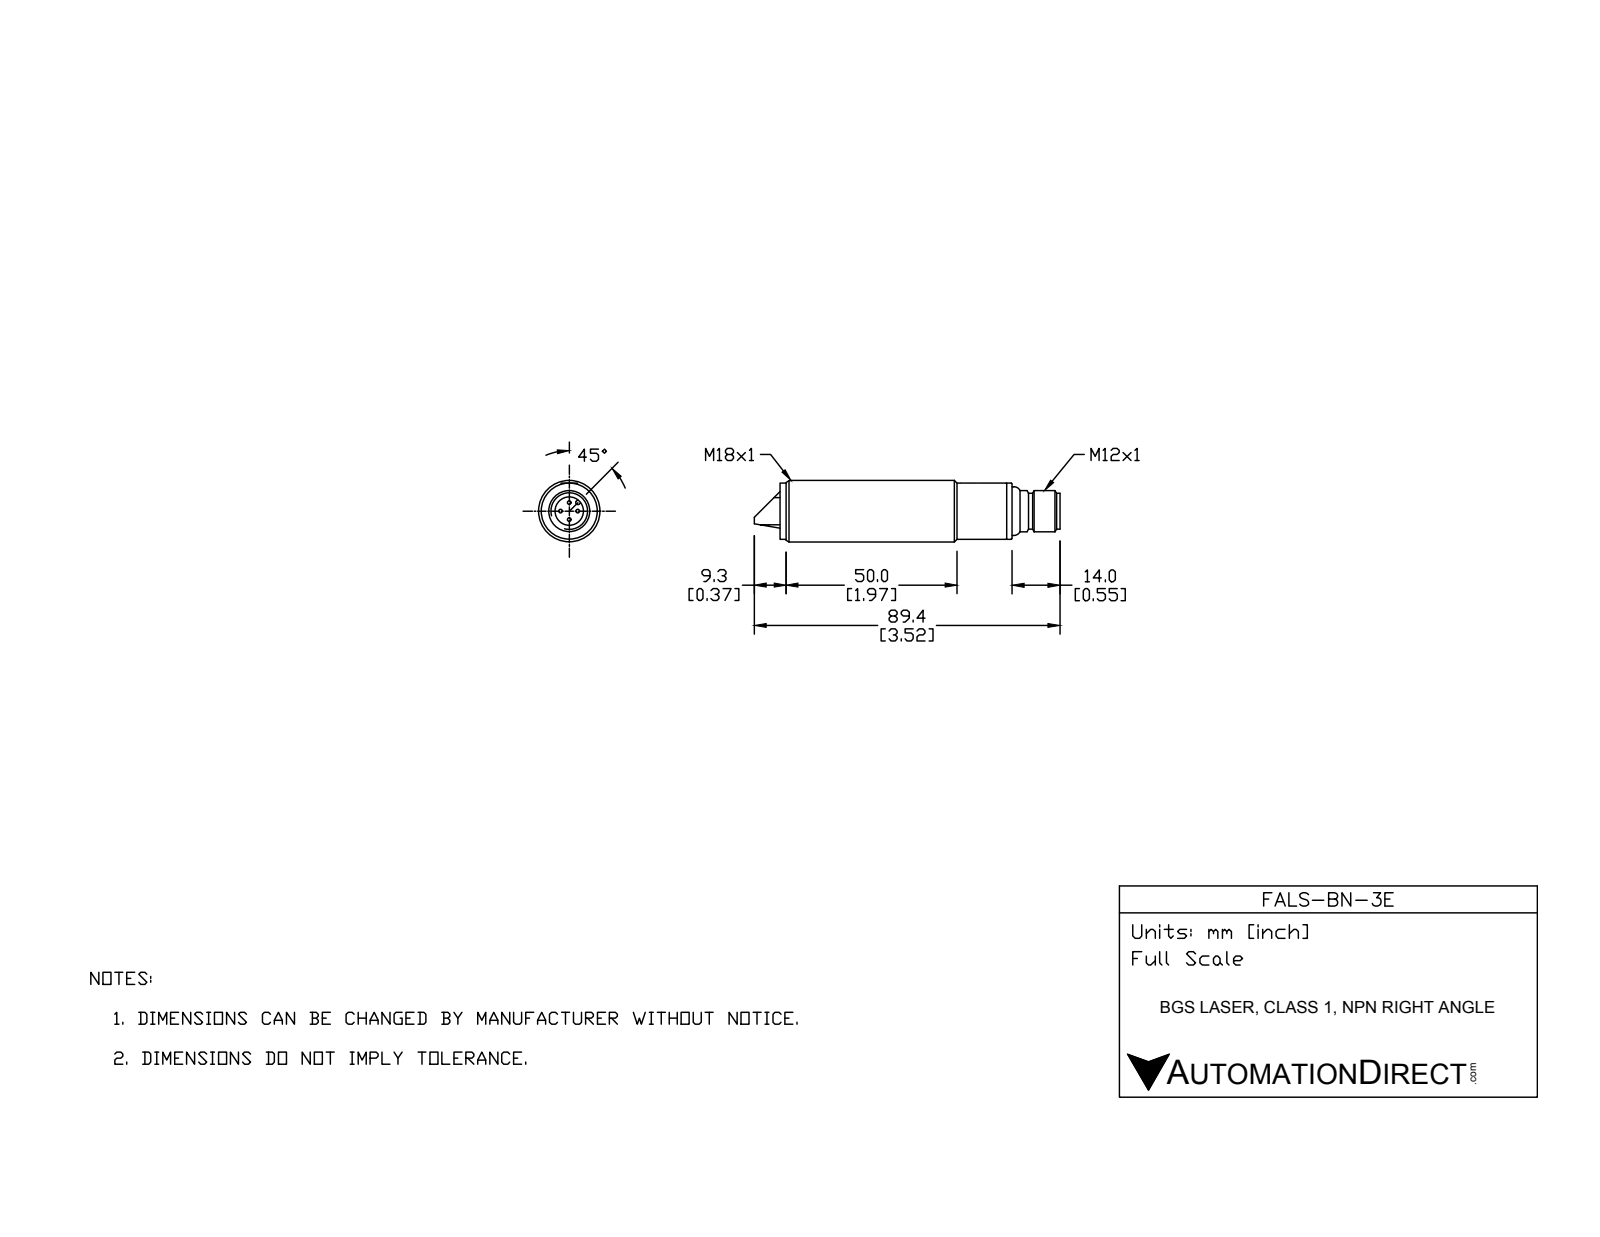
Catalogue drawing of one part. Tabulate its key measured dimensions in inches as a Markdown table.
| quantity | value |
| --- | --- |
| part name | FALS-BN-3E |
| STEP written by | SolidWorks 2017 (AUTOMOTIVE_DESIGN) |
| units | inches |
| bodies | 11 solids, 189 faces (63 planar, 81 cylindrical, 45 other) |
| overall size | 3.52 × 0.709 × 0.709 |
| volume | 1.096 in³ |
| surface area | 11.35 in² |
| round holes (diameter × count) | 0.039 × 4, 0.043 × 4, 0.106 × 1, 0.185 × 1, 0.278 × 1, 0.327 × 1, 0.591 × 1, 0.622 × 1 |
| round bosses / shafts (diameter × count) | 0.709 × 1, 0.65 × 1, 0.646 × 1, 0.559 × 1, 0.472 × 1, 0.413 × 1, 0.276 × 1, 0.189 × 1 |
| partial cylindrical surfaces (radius × count) | 0.02 × 4, 0.024 × 1, 0.317 × 1, 0.331 × 1 |
| main face-to-face distances | 0.039, 2.531, 0.071, 0.055, 2.476, 0.016, 2.461, 0.094, 0.11, 2.571 |
| hole center spacings | 0.098, 0.139, 0.197 |
